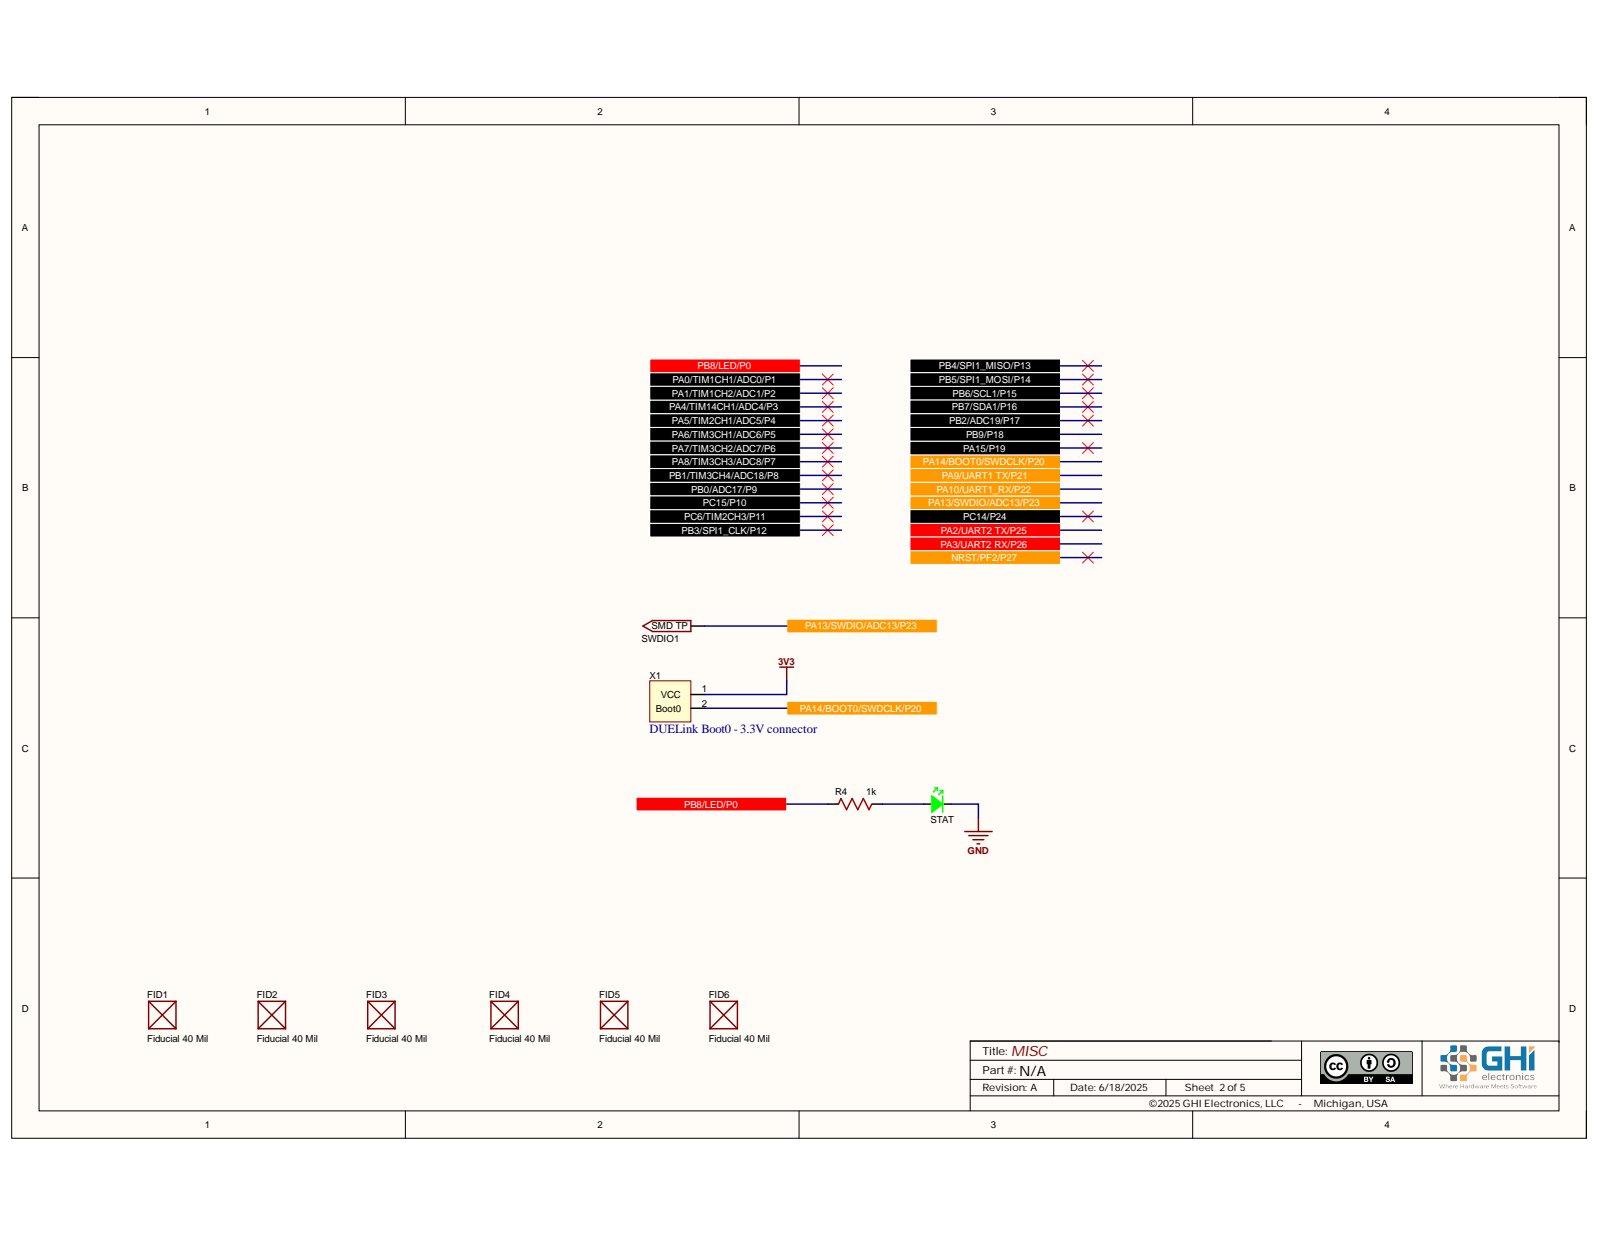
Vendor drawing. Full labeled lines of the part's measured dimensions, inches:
Part name (STEP PRODUCT): PCB; Board; U; DUELink-U-Connector-BM04B-SRSS-TB (+5 more)
STEP written by: Open CASCADE 7.5 (AUTOMOTIVE_DESIGN)
Units: inches
Bodies: 99 solids, 2191 faces (1407 planar, 504 cylindrical, 280 other)
Overall size (bounding box): 1.399 × 1.063 × 0.531
Volume: 0.17 in³ · Surface area: 6.615 in²
Round holes (diameter × count): ⌀0.035 ×4, ⌀0.04 ×2, ⌀0.118 ×2, ⌀0.102 ×1
Round bosses / shafts (diameter × count): ⌀0.016 ×3
Partial cylindrical surfaces — rounded edges, fillets, slot ends (radius × count): R0.004 ×135, R0.005 ×35, R0.006 ×14, R0.008 ×8, R0.01 ×6, R0.02 ×3, R0.007 ×2, R0.007 ×2
Main face-to-face distances: 0.063, 0.088, 0.151, 0.051, 0.458, 0.218, 0.177, 0.126, 0.407, 0.395
Hole centre spacings: 0.079, 0.157, 0.215, 0.317, 0.388, 0.461, 0.535, 0.58
